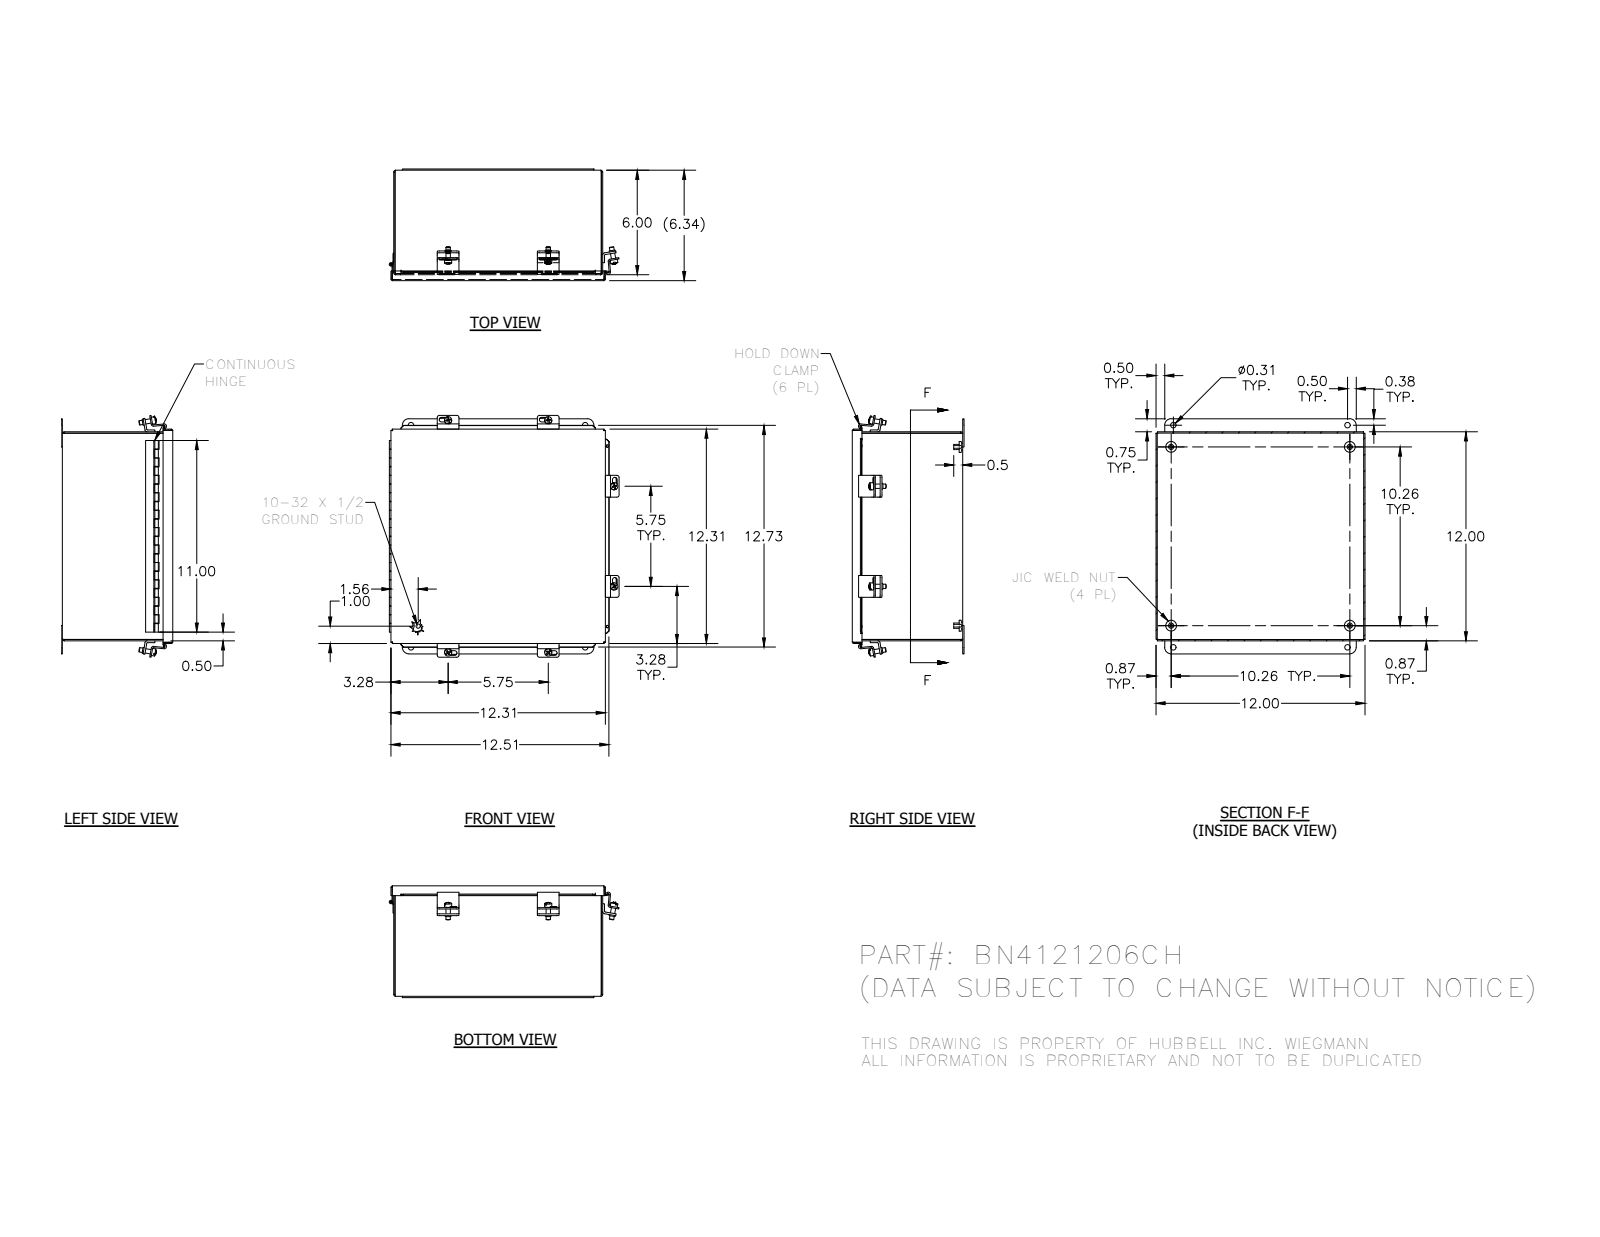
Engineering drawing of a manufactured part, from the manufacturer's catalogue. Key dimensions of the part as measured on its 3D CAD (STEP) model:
Part name (STEP PRODUCT): B_1212CH_LID; 316167; 38811; 3499 (+8 more)
STEP written by: Autodesk Inventor 2016 (AUTOMOTIVE_DESIGN)
Units: millimetres
Bodies: 20 solids, 507 faces (325 planar, 131 cylindrical, 51 other)
Overall size (bounding box): 342.9 × 332.38 × 158.98
Volume: 866 243 mm³ · Surface area: 944 402 mm²
Round holes (diameter × count): ⌀3.96 ×4, ⌀7.87 ×4, ⌀3.56 ×2, ⌀4.98 ×2, ⌀2.96 ×1
Round bosses / shafts (diameter × count): ⌀15.88 ×4, ⌀7.62 ×4, ⌀6.35 ×3, ⌀10.4 ×2, ⌀8.74 ×2, ⌀5.08 ×1, ⌀4.83 ×1, ⌀2.54 ×1
Partial cylindrical surfaces — rounded edges, fillets, slot ends (radius × count): R1.19 ×8, R3.07 ×8, R3.17 ×8, R1.98 ×4, R3.38 ×4, R3.48 ×4, R9.53 ×4, R0.79 ×3
Main face-to-face distances: 1.88, 302.92, 155.58, 1.5, 157.08, 153.7, 155.2, 304.8, 301.04, 1.9
Hole centre spacings: 31.91, 260.35, 292.12, 389.18, 254, 259.12, 259.13, 323.85
